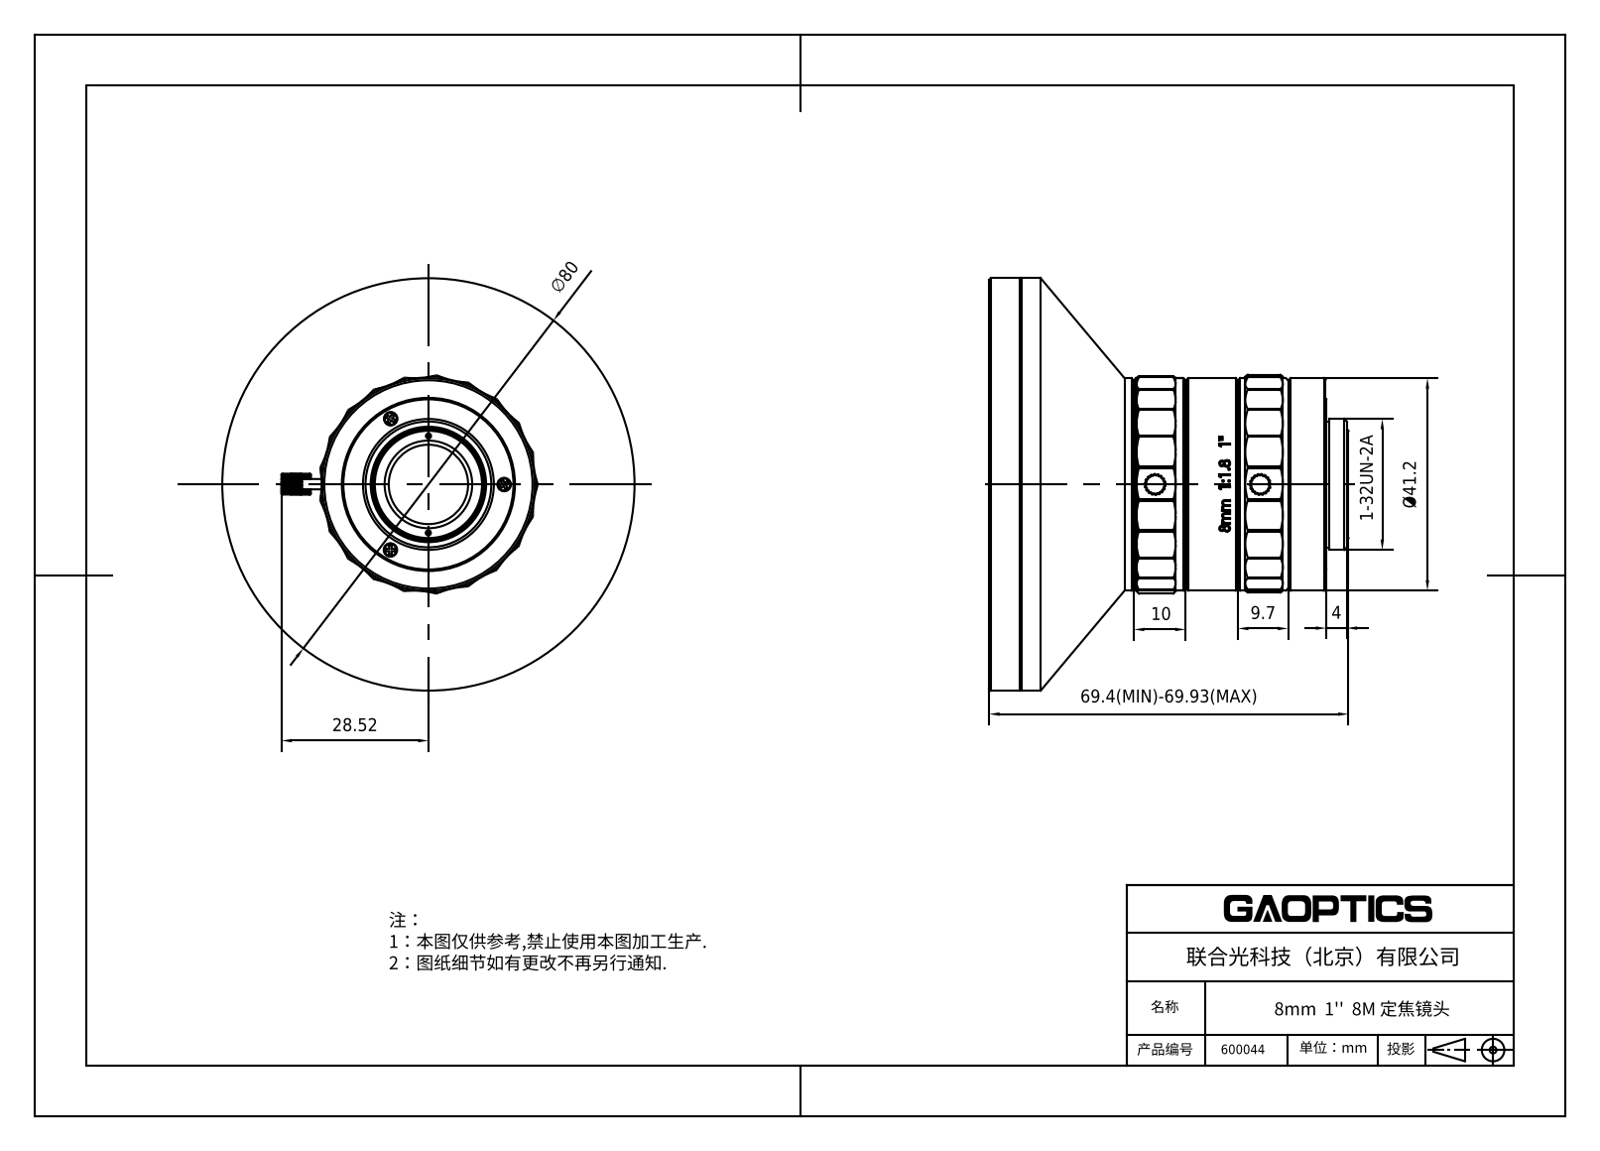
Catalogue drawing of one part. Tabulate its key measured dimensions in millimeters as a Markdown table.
| quantity | value |
| --- | --- |
| part name | 680044 |
| STEP written by | SolidWorks 2020 (CONFIG_CONTROL_DESIGN) |
| units | millimeters |
| bodies | 0 solids, 1701 faces (411 planar, 477 cylindrical, 813 other) |
| overall size | 80 × 80 × 69.73 |
| round holes (diameter × count) | 1.6 × 8, 1.2 × 6, 1.25 × 3, 1.7 × 3, 2.6 × 3, 3.2 × 3, 1 × 2, 2.8 × 2, 1.5 × 1, 8.6 × 1, 9.4 × 1, 9.6 × 1 |
| round bosses / shafts (diameter × count) | 2 × 6, 2.8 × 3, 80 × 1, 79.9 × 1, 53 × 1, 41.2 × 1, 32.4 × 1, 31.2 × 1 |
| partial cylindrical surfaces (radius × count) | 0.5 × 42, 17.5 × 42, 1.5 × 18, 2 × 5, 0.8 × 1, 10.75 × 1, 18 × 1, 18.2 × 1 |
| main face-to-face distances | 4.81, 53.58, 48.77, 7.54, 2.73, 46.04, 7.31, 2.5, 46.27, 7.72 |
| hole center spacings | 9.54, 14.45, 16.53, 5.52, 14.7, 24.16, 25.46, 3.37 |
